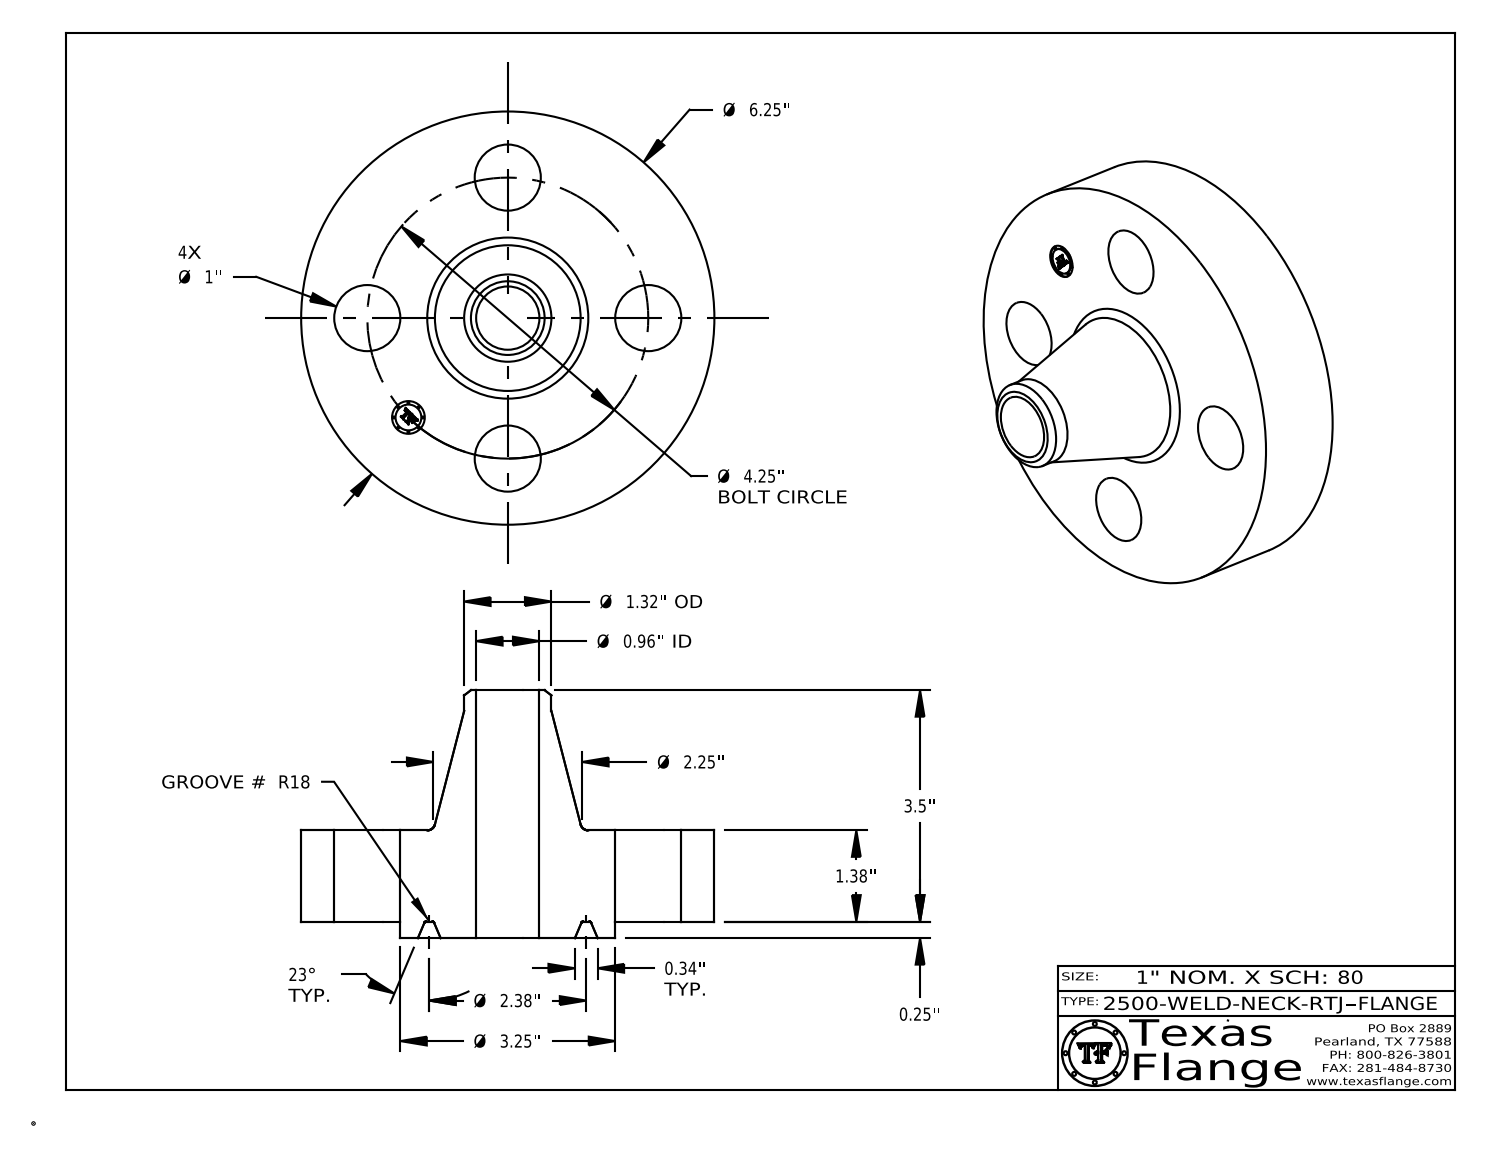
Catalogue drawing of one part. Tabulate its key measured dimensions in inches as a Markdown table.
| quantity | value |
| --- | --- |
| part name | 2500-WELD-NECK-RTJ |
| STEP written by | CATIA V5 STEP AP214 (AUTOMOTIVE_DESIGN) |
| units | inches |
| bodies | 1 solid, 421 faces (371 planar, 36 cylindrical, 14 other) |
| overall size | 6.25 × 6.25 × 3.75 |
| volume | 41.98 in³ |
| surface area | 123.1 in² |
| round holes (diameter × count) | 1 × 4, 0.495 × 1, 0.957 × 1 |
| round bosses / shafts (diameter × count) | 0.03 × 8, 6.25 × 1, 3.25 × 1, 1.32 × 1, 0.39 × 1 |
| main face-to-face distances | 1.38, 0.25, 1.63, 3.75, 3.5, 2.12, 1.615, 1.365, 0.015, 2.135 |
| hole center spacings | 2.125, 3.006, 1.626, 3.927, 4.25 |
